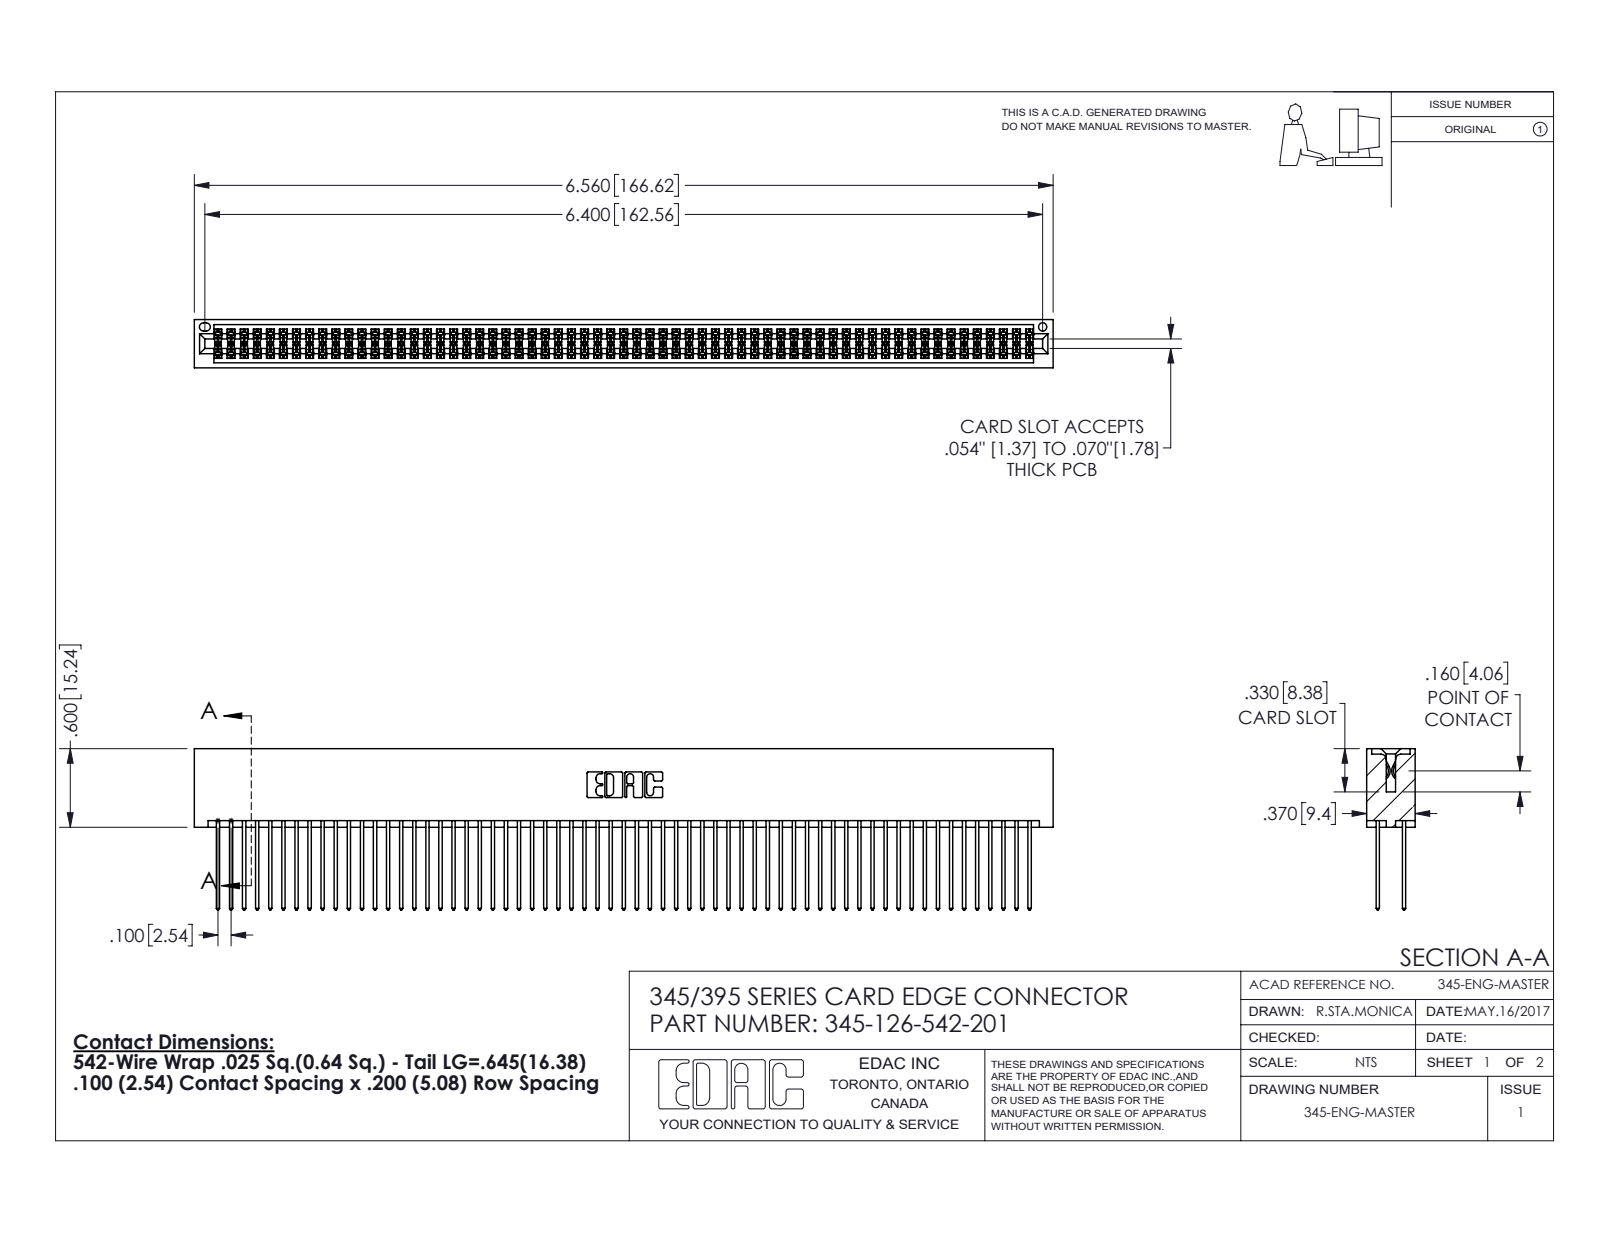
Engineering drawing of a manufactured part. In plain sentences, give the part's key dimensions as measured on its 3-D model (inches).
The part is named "345 Part_No Mounting Lugs; 345-126-542-201; 345-292-001_345-293-142". Its 3-D file was written by "SolidWorks 2016 (CONFIG_CONTROL_DESIGN)". It is 127 solids with 6418 faces: 4234 planar, 2184 cylindrical and 0 other. Overall it measures 6.56 by 1.232 by 0.37 inches. Its volume is 1.073 cubic inches and its surface area 45.64 square inches. Round holes: 1 of diameter 0.064. Partial cylindrical surfaces (rounded edges, fillets, slot ends): 189 of radius 0.006, 126 of radius 0.01, 22 of radius 0.01, 6 of radius 0.007, 6 of radius 0.031, 3 of radius 0.026, 2 of radius 0.014, 2 of radius 0.019. The main face-to-face distances are 0.298, 0.072, 0.2, 0.098, 0.272, 0.025, 0.225, 0.37, 0.175, 0.149.
